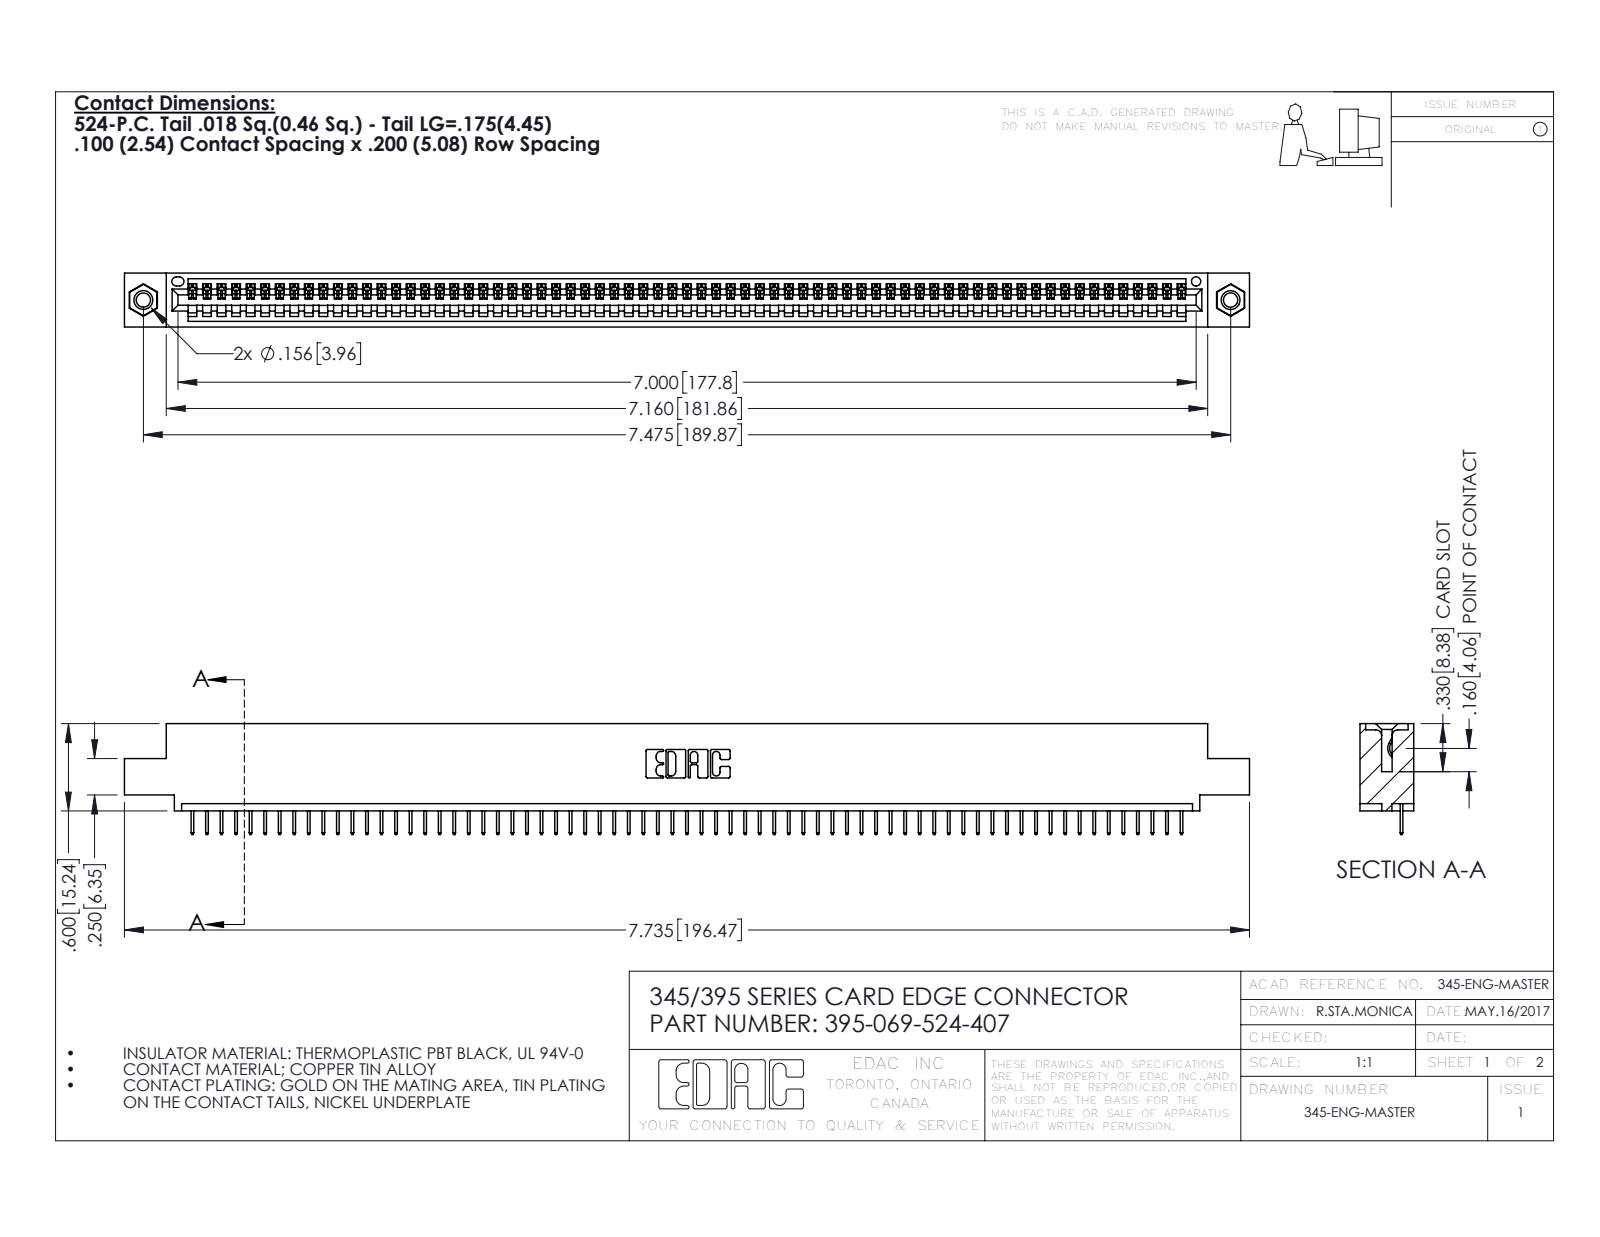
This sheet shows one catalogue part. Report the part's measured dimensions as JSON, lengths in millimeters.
{"part_name": "395-069-524-407; 345-292-001_345-293-124; 345 Part_0.110 Offset - 0.156 Dia-TI; 345-250-001_345-250-005-103", "step_written_by": "SolidWorks 2016 (CONFIG_CONTROL_DESIGN)", "units": "millimeters", "bodies": {"solids": 72, "faces": 4468, "planar": 3290, "cylindrical": 1162, "other": 16}, "overall_size": [196.5, 19.4, 9.4], "volume_mm3": 18520, "surface_area_mm2": 24230, "round_holes": [[2.5, 2], [3.2, 2], [4, 2], [1.6, 1]], "round_bosses_or_shafts": [[3.9, 2]], "partial_cylinders_radius": [[0.2, 138], [0.3, 22], [0.2, 6], [0.8, 6], [0.7, 3], [0.8, 2], [1, 2], [0.4, 1]], "face_to_face_distances": [1.8, 7.6, 9.4, 5.1, 2.5, 6.9, 0.6, 5.7, 1.8, 3.8], "hole_center_spacings": [6.9, 183.9, 189.9]}
